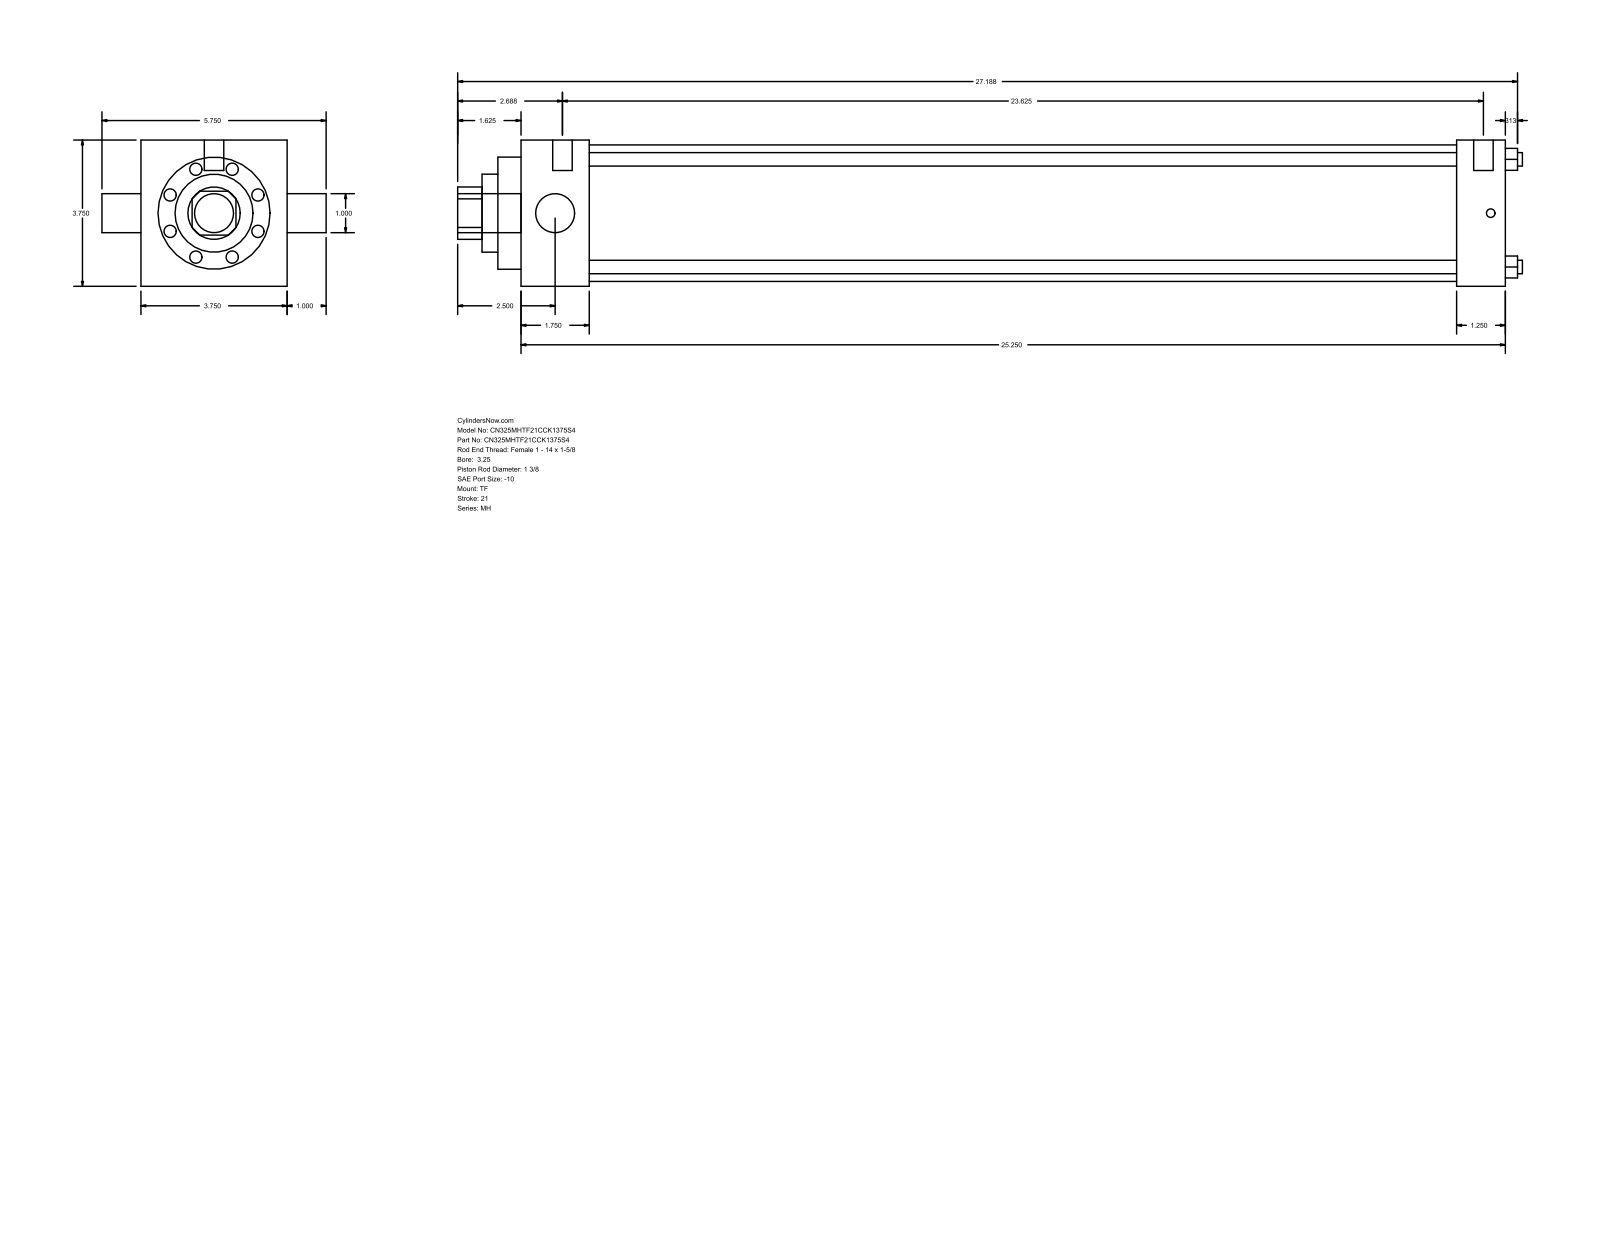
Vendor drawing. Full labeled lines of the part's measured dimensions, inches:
Part name (STEP PRODUCT): MH_TF__0325_1.375
STEP written by: GSSL Pune (CONFIG_CONTROL_DESIGN)
Units: inches
Bodies: 0 solids, 86 faces (61 planar, 25 cylindrical, 0 other)
Overall size (bounding box): 27.313 × 5.75 × 3.75
Round holes (diameter × count): ⌀0.345 ×4, ⌀1 ×1, ⌀1.375 ×1, ⌀2 ×1, ⌀2.875 ×1, ⌀3.5 ×1
Round bosses / shafts (diameter × count): ⌀0.219 ×3, ⌀0.5 ×2, ⌀1 ×1
Partial cylindrical surfaces — rounded edges, fillets, slot ends (radius × count): R0.672 ×1
Main face-to-face distances: 3.75, 25.25, 1.75, 24, 22.25, 23.5, 1.25, 0.594, 2.344, 24.594
Hole centre spacings: 1.952, 2.76, 3.903
